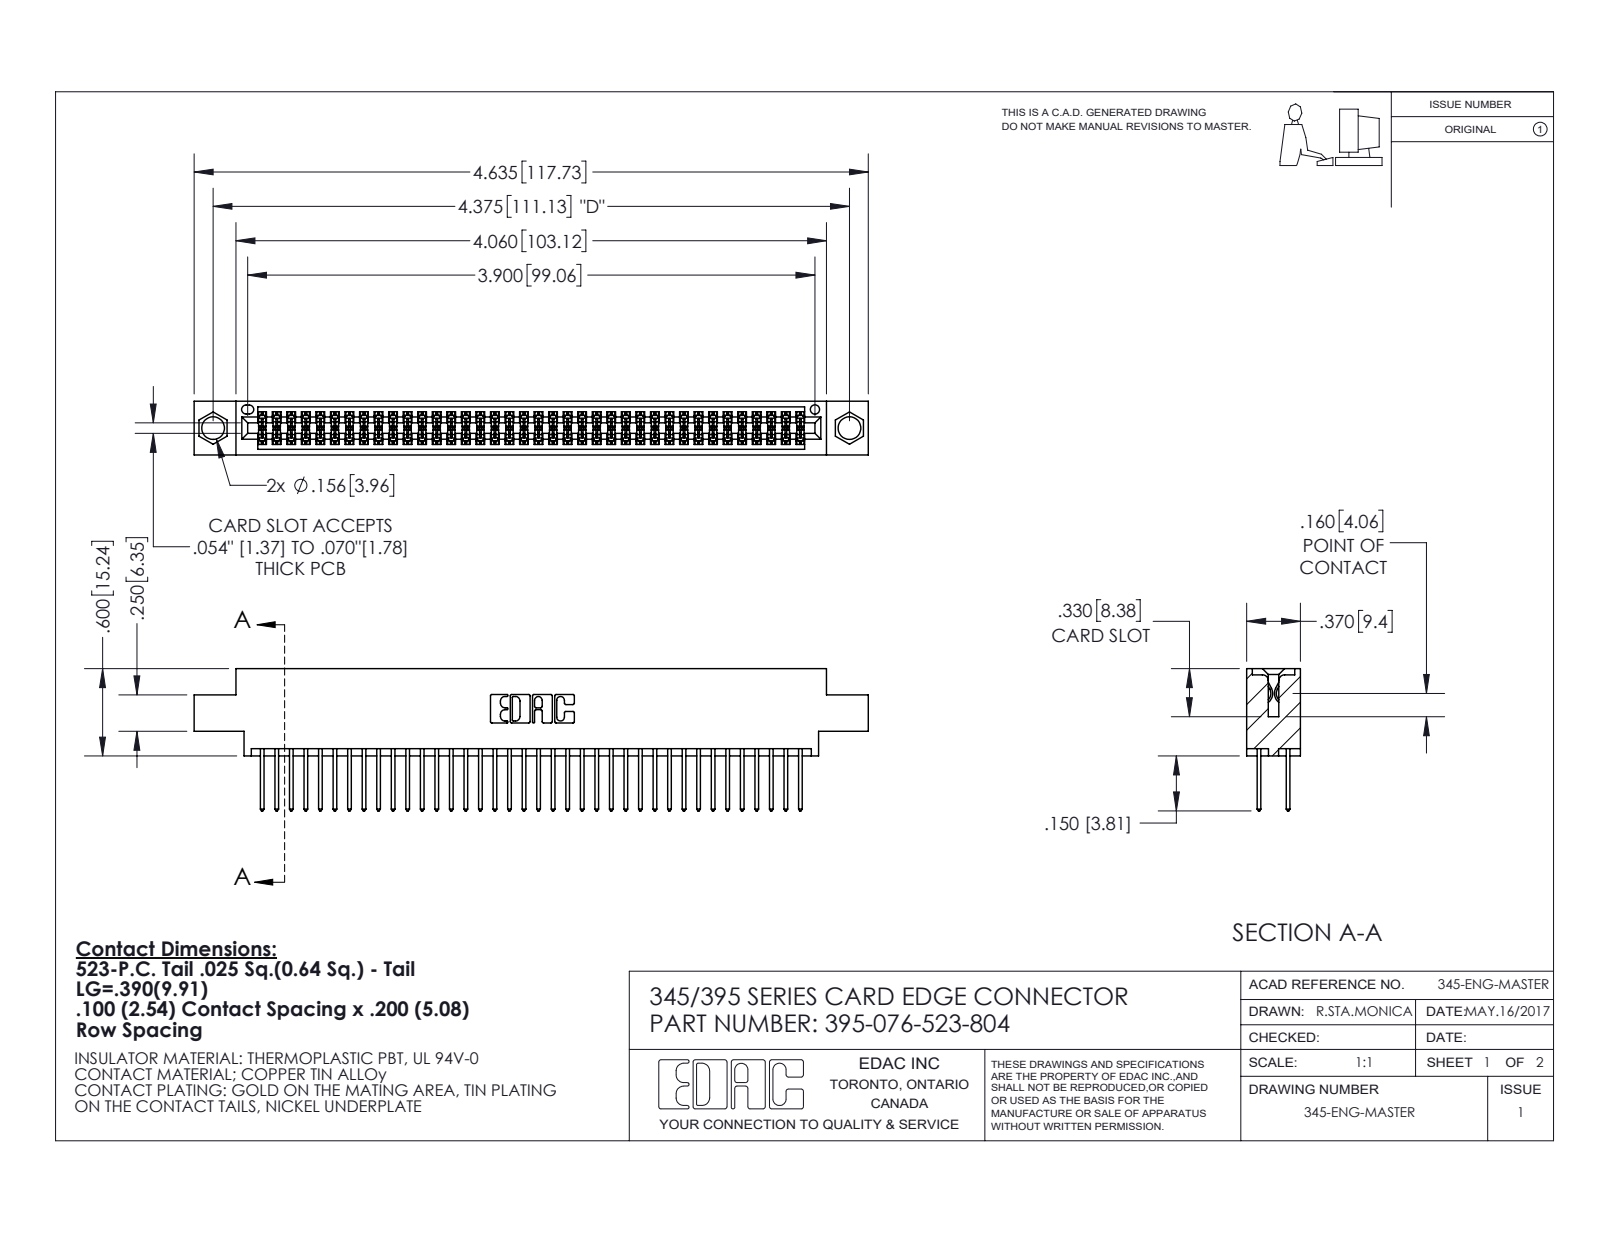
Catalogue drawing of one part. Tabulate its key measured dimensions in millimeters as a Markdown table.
| quantity | value |
| --- | --- |
| part name | 345-292-001_345-293-123; 345 Part_0.170 Offset - 0.156 Dia-TI; 395-076-523-804 |
| STEP written by | SolidWorks 2020 (CONFIG_CONTROL_DESIGN) |
| units | millimeters |
| bodies | 77 solids, 3944 faces (2606 planar, 1338 cylindrical, 0 other) |
| overall size | 117.7 × 24.8 × 9.4 |
| volume | 11 300 mm³ |
| surface area | 17 370 mm² |
| round holes (diameter × count) | 4 × 2, 1.6 × 1 |
| partial cylindrical surfaces (radius × count) | 0.2 × 114, 0.3 × 76, 0.3 × 22, 0.2 × 6, 0.8 × 6, 0.7 × 3, 0.4 × 2, 0.5 × 2 |
| main face-to-face distances | 1.8, 7.6, 5.1, 2.5, 6.9, 0.6, 9.4, 5.7, 4.4, 3.8 |
| hole center spacings | 6.9, 105.1, 111.1 |
